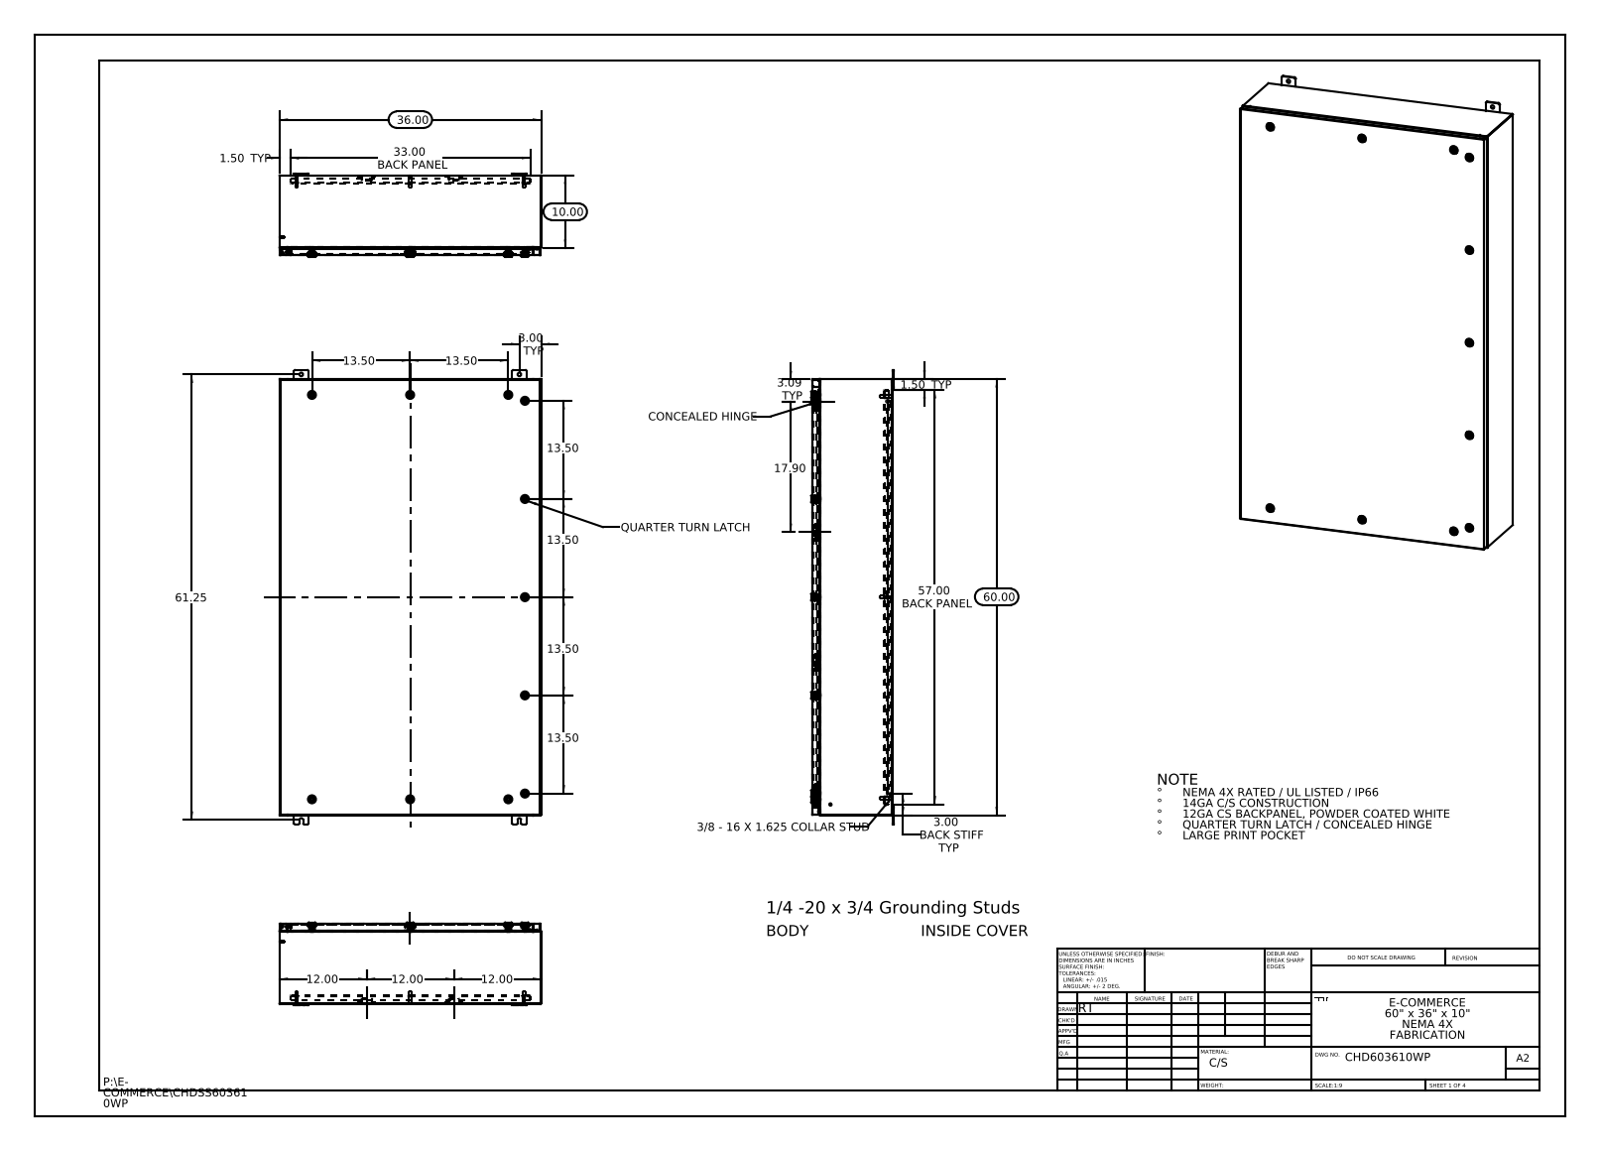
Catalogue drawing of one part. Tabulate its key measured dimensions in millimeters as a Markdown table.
| quantity | value |
| --- | --- |
| part name | CHDSS603610WP Mounting Studs; Quarter-20 CD Stud; CHDSS603610WP Mounting Feet; Insert-221320-IB-Industrilas_Insert-221320-IB-Industrilas (+8 more) |
| STEP written by | SolidWorks 2013 (CONFIG_CONTROL_DESIGN) |
| units | millimeters |
| bodies | 104 solids, 9960 faces (2880 planar, 3110 cylindrical, 3970 other) |
| overall size | 1587.5 × 914.4 × 288.4 |
| volume | 12 610 000 mm³ |
| surface area | 12 280 000 mm² |
| round holes (diameter × count) | 12.7 × 12, 5 × 11, 10 × 11, 10.2 × 11, 16 × 11, 20 × 11, 3.5 × 8, 6.4 × 8, 5.4 × 1 |
| round bosses / shafts (diameter × count) | 6 × 13, 28 × 11, 19.8 × 11, 15.9 × 11, 15.5 × 11, 13.5 × 11, 10 × 11, 2.9 × 11 |
| partial cylindrical surfaces (radius × count) | 0.2 × 363, 3 × 363, 0.7 × 132, 0.5 × 44, 5 × 44, 0.3 × 34, 2.2 × 30, 4.8 × 24 |
| main face-to-face distances | 1.9, 1.9, 275.9, 277.8, 279.7, 277.7, 2.6, 25.4, 27.3, 250.5 |
| hole center spacings | 342.9, 454.6, 17.5, 56.5, 685.8, 701.7, 909.1, 1059.4 |
